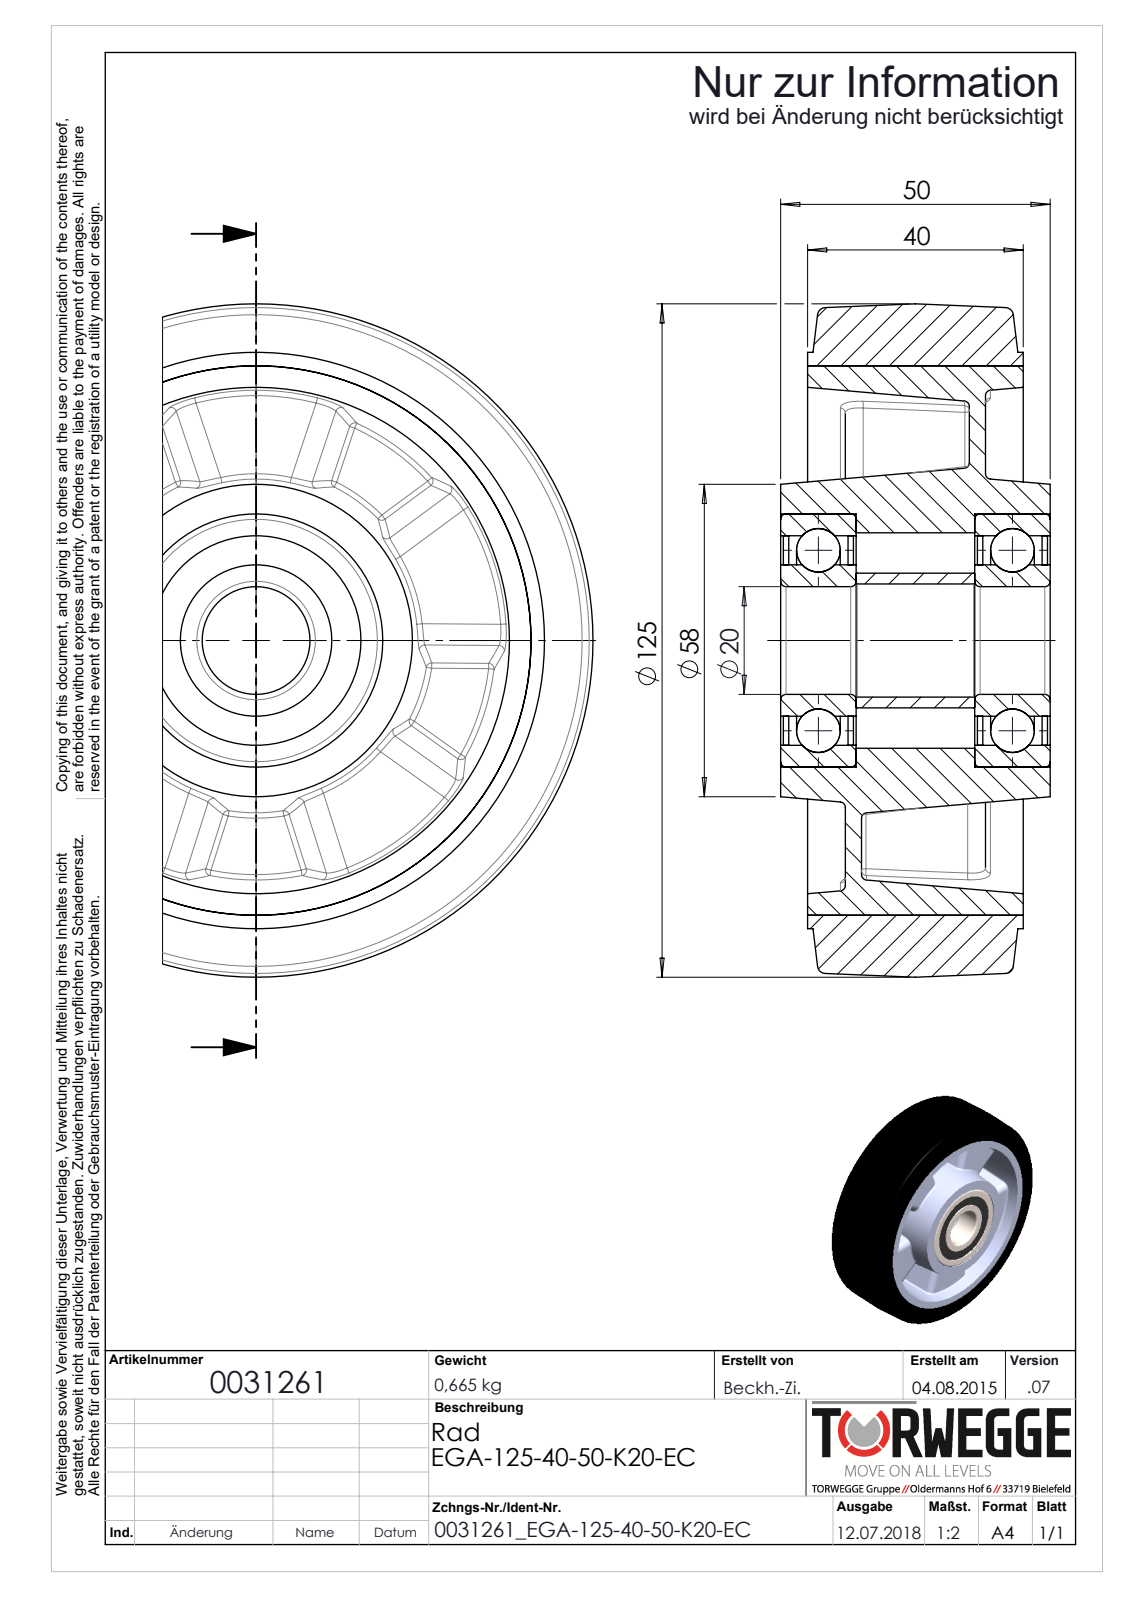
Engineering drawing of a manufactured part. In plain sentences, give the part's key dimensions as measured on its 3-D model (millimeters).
The part is named "0031261_EGA-125-40-50-K20-EC". Its 3-D file was written by "SolidWorks 2016 (AUTOMOTIVE_DESIGN)". It is 9 solids with 396 faces: 66 planar, 98 cylindrical and 232 other. Overall it measures 125 by 125 by 50 millimeters. Its volume is 341 516 cubic millimeters and its surface area 112 589 square millimeters. Round holes: 1 of diameter 20, 1 of diameter 21, 1 of diameter 28.1, 1 of diameter 38.9, 1 of diameter 40, 1 of diameter 47, 1 of diameter 102. Round bosses or shafts: 1 of diameter 107, 1 of diameter 25. Partial cylindrical surfaces (rounded edges, fillets, slot ends): 20 of radius 1, 20 of radius 4. The main face-to-face distances are 12, 36, 1.5, 1, 24, 0.5, 13.5, 5, 45, 38.
